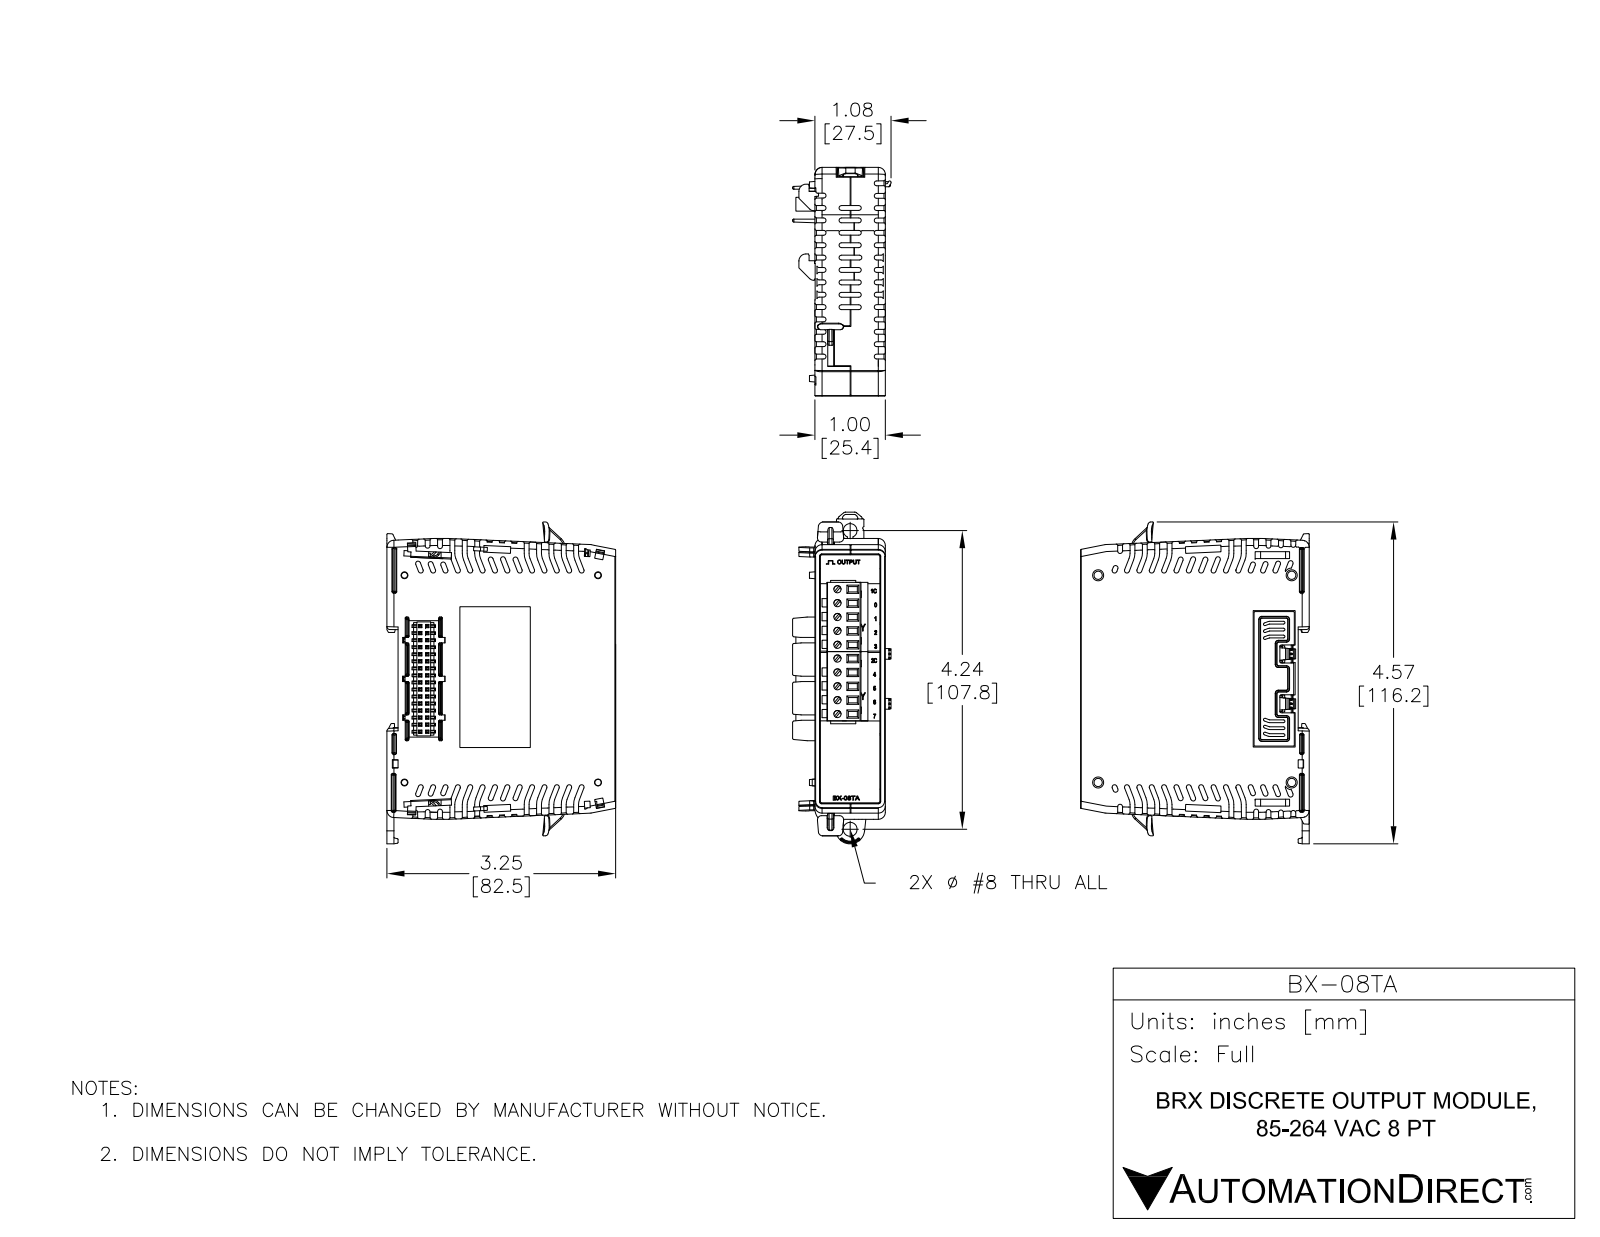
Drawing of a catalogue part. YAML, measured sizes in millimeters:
part_name: "BX-08TA"
step_written_by: "SolidWorks 2017 (AUTOMOTIVE_DESIGN)"
units: millimeters
bodies: {solids: 22, faces: 3574, planar: 2540, cylindrical: 563, other: 471}
overall_size: [116.5, 84.1, 35.6]
volume: 189900
surface_area: 46940
round_holes:
  - {diameter: 1.2, count: 2}
  - {diameter: 1.7, count: 2}
  - {diameter: 3, count: 2}
  - {diameter: 3, count: 2}
  - {diameter: 5.1, count: 1}
round_bosses_or_shafts:
  - {diameter: 1.6, count: 2}
  - {diameter: 1.5, count: 2}
partial_cylinders:
  - {radius: 0.1, count: 102}
  - {radius: 0.3, count: 47}
  - {radius: 0.5, count: 34}
  - {radius: 0.1, count: 24}
  - {radius: 0.2, count: 21}
  - {radius: 3, count: 14}
  - {radius: 1, count: 13}
  - {radius: 0.3, count: 12}
face_to_face_distances: [25.4, 81.6, 81.8, 12.1, 2.5, 4, 77.5, 77.8, 20, 16]
hole_center_spacings: [2.5, 20.9, 23.3, 33, 53.2, 55.7, 65.7, 66.5]
